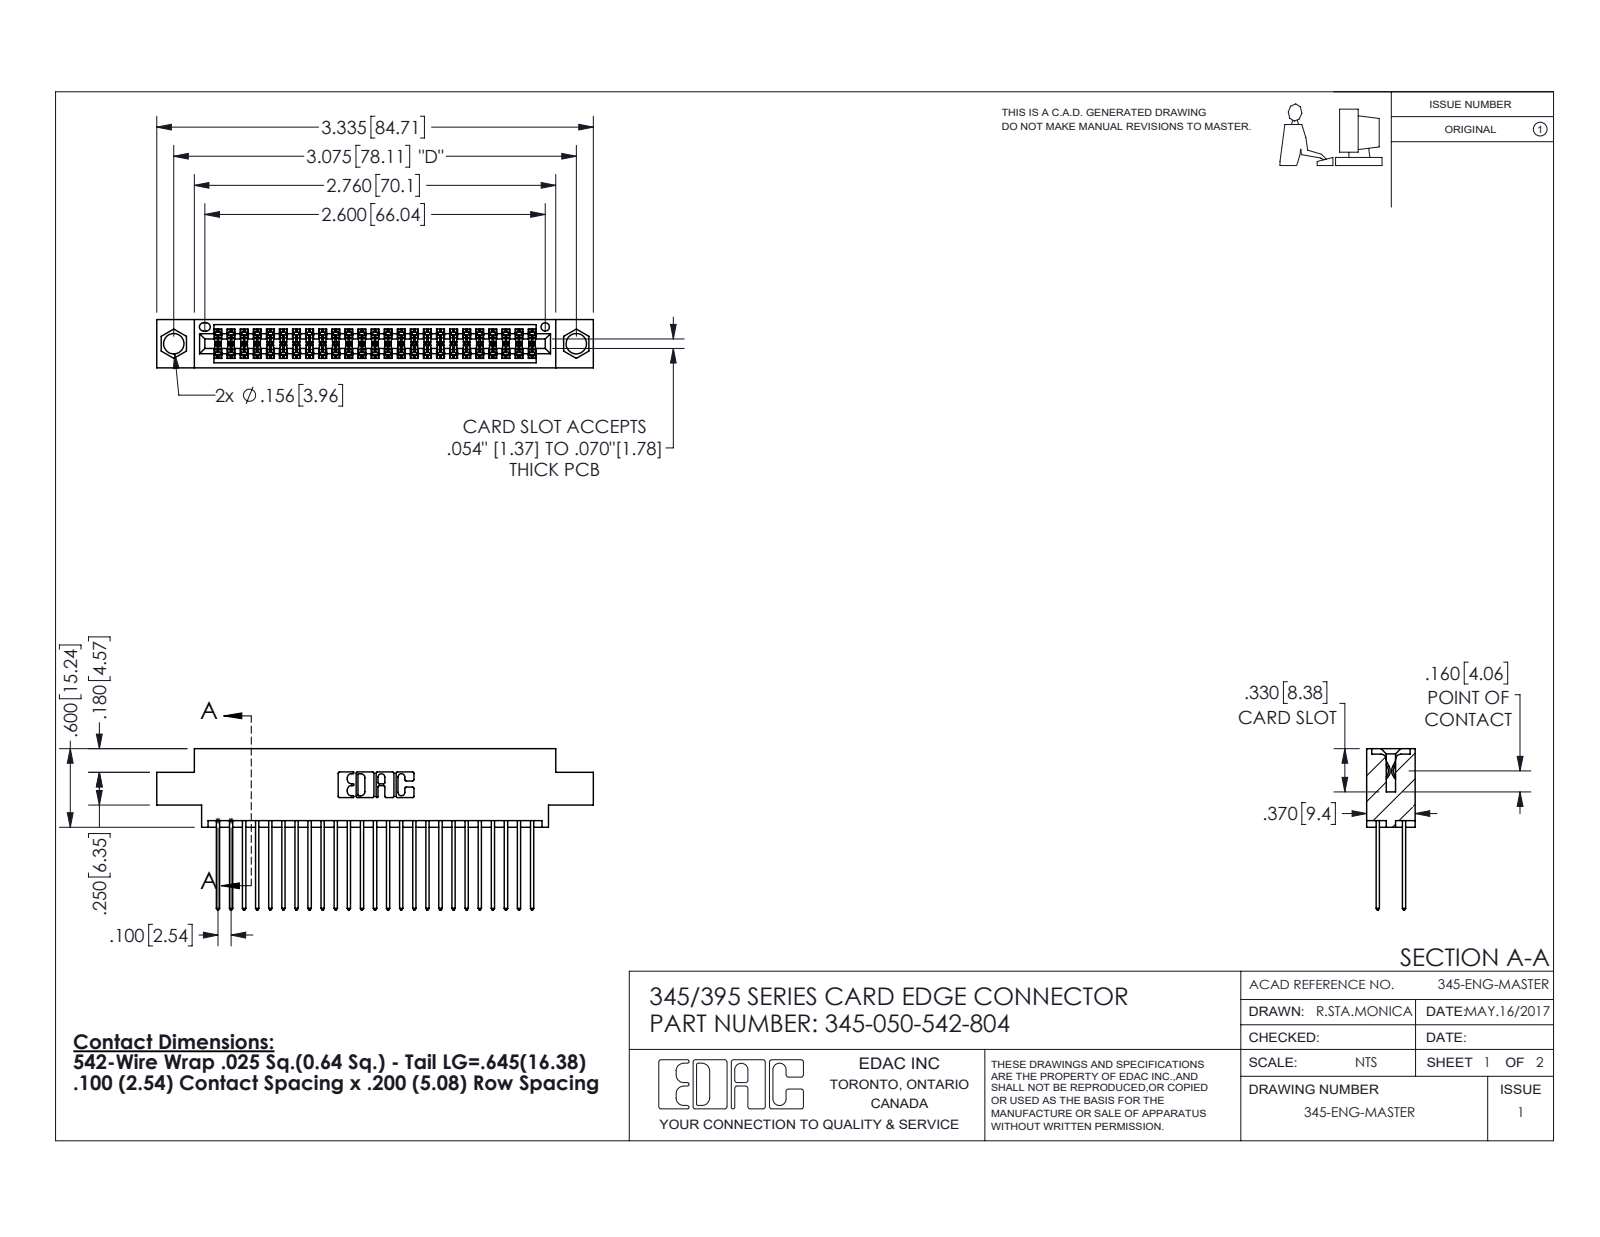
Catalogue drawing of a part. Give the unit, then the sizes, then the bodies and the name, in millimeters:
Units: millimetres
Overall size (bounding box): 84.7 × 31.3 × 9.4
Round holes (diameter × count): ⌀4 ×2, ⌀1.6 ×1
Partial cylindrical surfaces — rounded edges, fillets, slot ends (radius × count): R0.2 ×75, R0.3 ×50, R0.3 ×22, R0.2 ×6, R0.8 ×6, R0.7 ×3, R0.4 ×2, R0.5 ×2
Main face-to-face distances: 1.8, 7.6, 5.1, 2.5, 6.9, 0.6, 9.4, 5.7, 4.4, 3.8
Hole centre spacings: 6.9, 72.1, 78.1
Volume: 8 080 mm³ · Surface area: 12 700 mm²
Bodies: 51 solids, 2644 faces (1748 planar, 896 cylindrical, 0 other)
Part name (STEP PRODUCT): 345-050-542-804; 345 Part_0.170 Offset - 0.156 Dia-TI; 345-292-001_345-293-142
STEP written by: SolidWorks 2020 (CONFIG_CONTROL_DESIGN)
